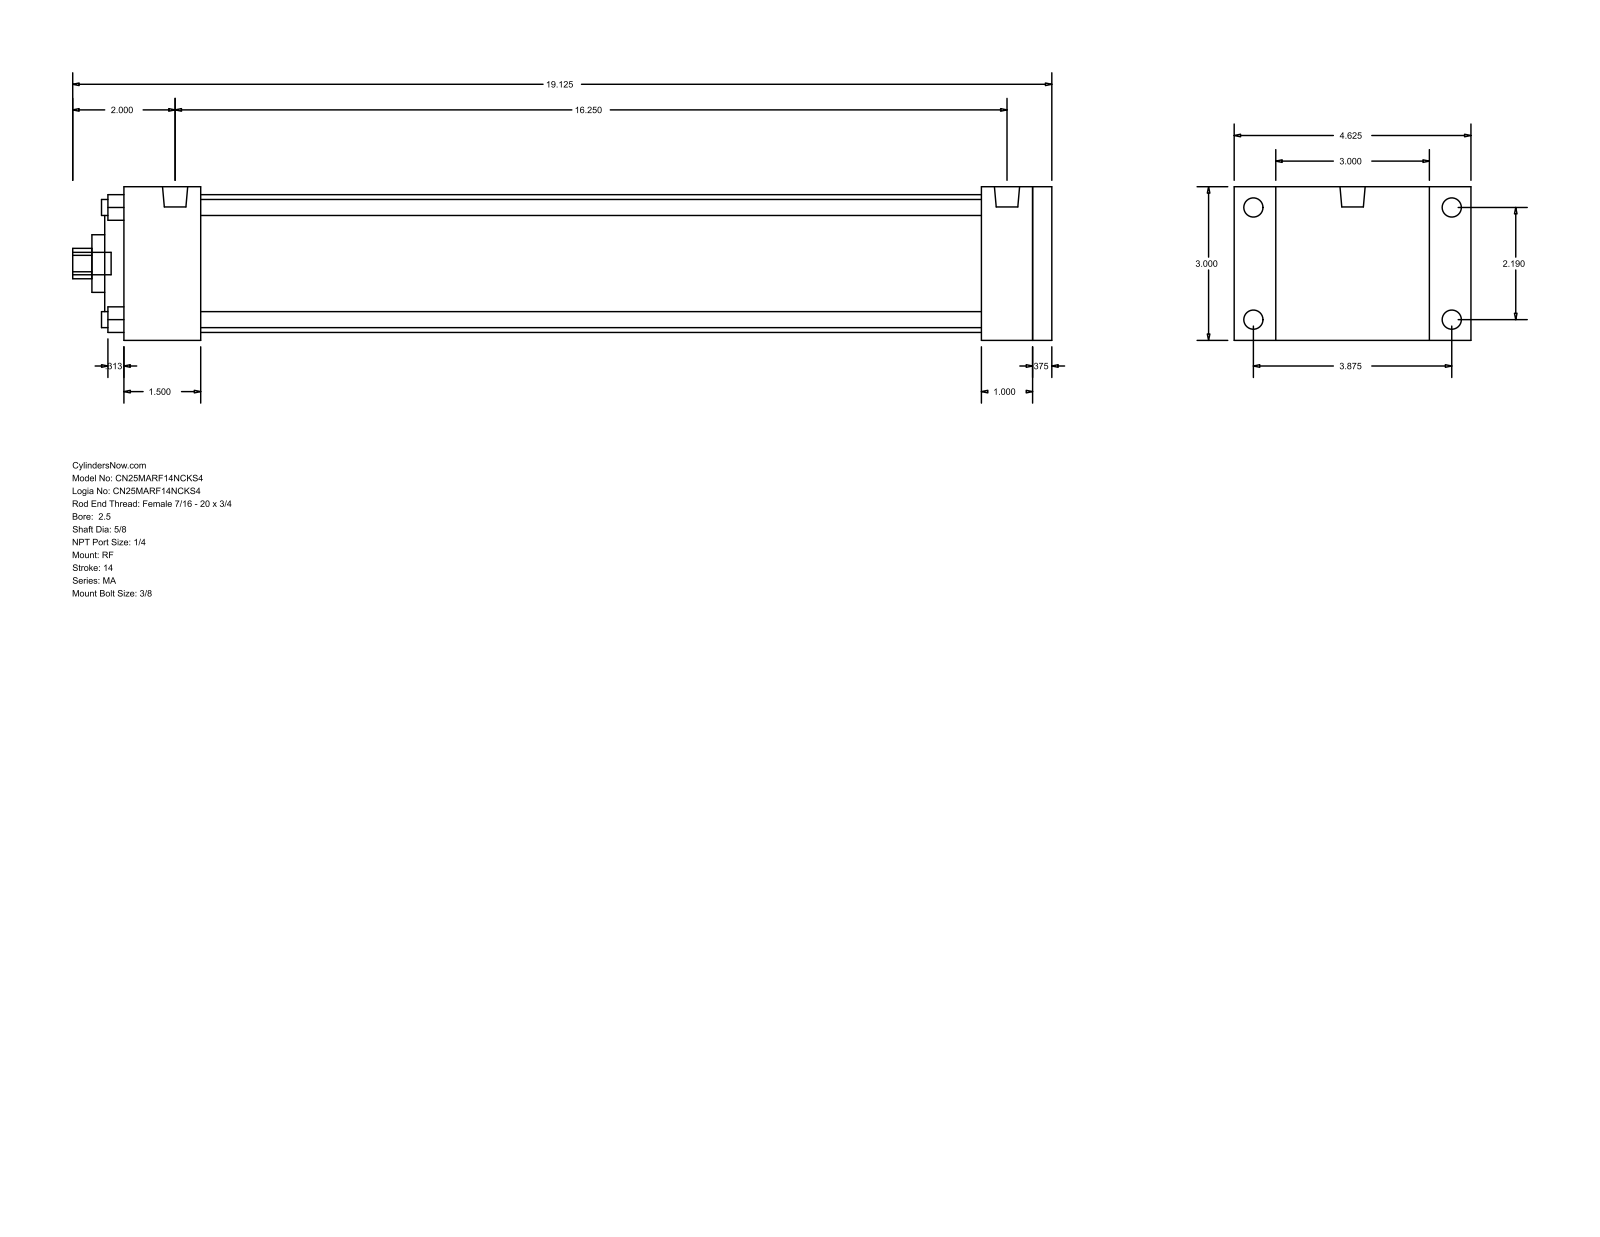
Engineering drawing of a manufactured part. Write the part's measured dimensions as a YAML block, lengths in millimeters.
part_name: "MA_RF__0250_0.625"
step_written_by: "GSSL Pune (CONFIG_CONTROL_DESIGN)"
units: millimeters
bodies: {solids: 0, faces: 94, planar: 65, cylindrical: 29, other: 0}
overall_size: [485.77, 117.47, 76.2]
round_holes:
  - {diameter: 7.94, count: 4}
  - {diameter: 15.88, count: 1}
  - {diameter: 28.57, count: 1}
  - {diameter: 50.8, count: 1}
  - {diameter: 68.33, count: 1}
round_bosses_or_shafts:
  - {diameter: 9.53, count: 4}
  - {diameter: 7.94, count: 4}
  - {diameter: 12.49, count: 2}
  - {diameter: 11.11, count: 1}
partial_cylinders:
  - {radius: 7.54, count: 1}
face_to_face_distances: [76.2, 460.37, 9.52, 450.85, 25.4, 38.1, 425.45, 387.35, 412.75, 422.27]
hole_center_spacings: [39.33, 55.62, 78.66]
